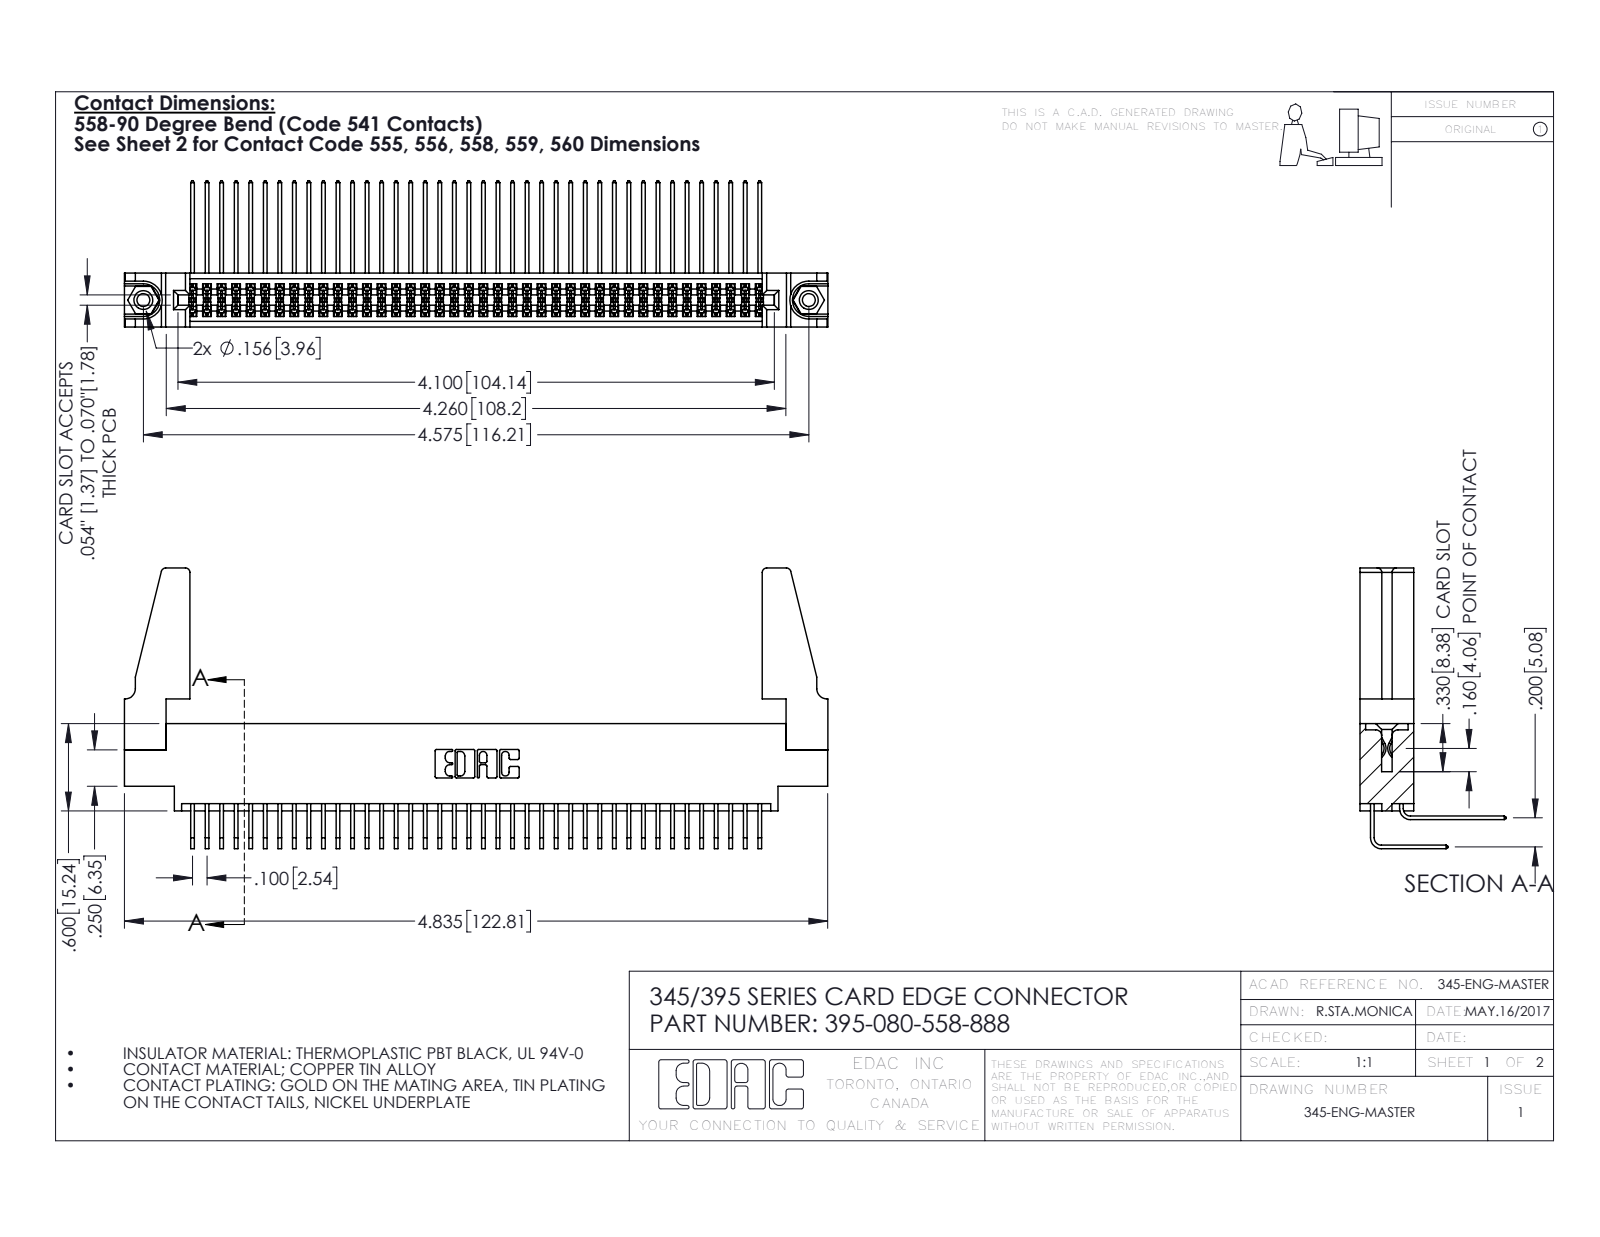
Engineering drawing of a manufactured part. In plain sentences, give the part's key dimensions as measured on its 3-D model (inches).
The part is named "345 Part_0.170 Offset - 0.156 Dia-TH; 395-080-558-888; 345-220-078_345-220-088; 345-292-001_558 559 Tail - 1 (+2 more)". Its 3-D file was written by "SolidWorks 2016 (CONFIG_CONTROL_DESIGN)". It is 85 solids with 4414 faces: 2956 planar, 1442 cylindrical and 16 other. Overall it measures 4.836 by 1.929 by 1.005 inches. Its volume is 0.947 cubic inches and its surface area 36.46 square inches. Round holes: 2 of diameter 0.089, 2 of diameter 0.125, 2 of diameter 0.156, 1 of diameter 0.064. Round bosses or shafts: 2 of diameter 0.155. Partial cylindrical surfaces (rounded edges, fillets, slot ends): 121 of radius 0.006, 22 of radius 0.01, 8 of radius 0.03, 6 of radius 0.007, 6 of radius 0.031, 3 of radius 0.026, 2 of radius 0.014, 2 of radius 0.019. The main face-to-face distances are 0.072, 0.298, 0.37, 0.2, 0.098, 0.272, 0.025, 0.225, 0.175, 0.025. The hole center spacings are 0.27, 4.339, 4.575.
